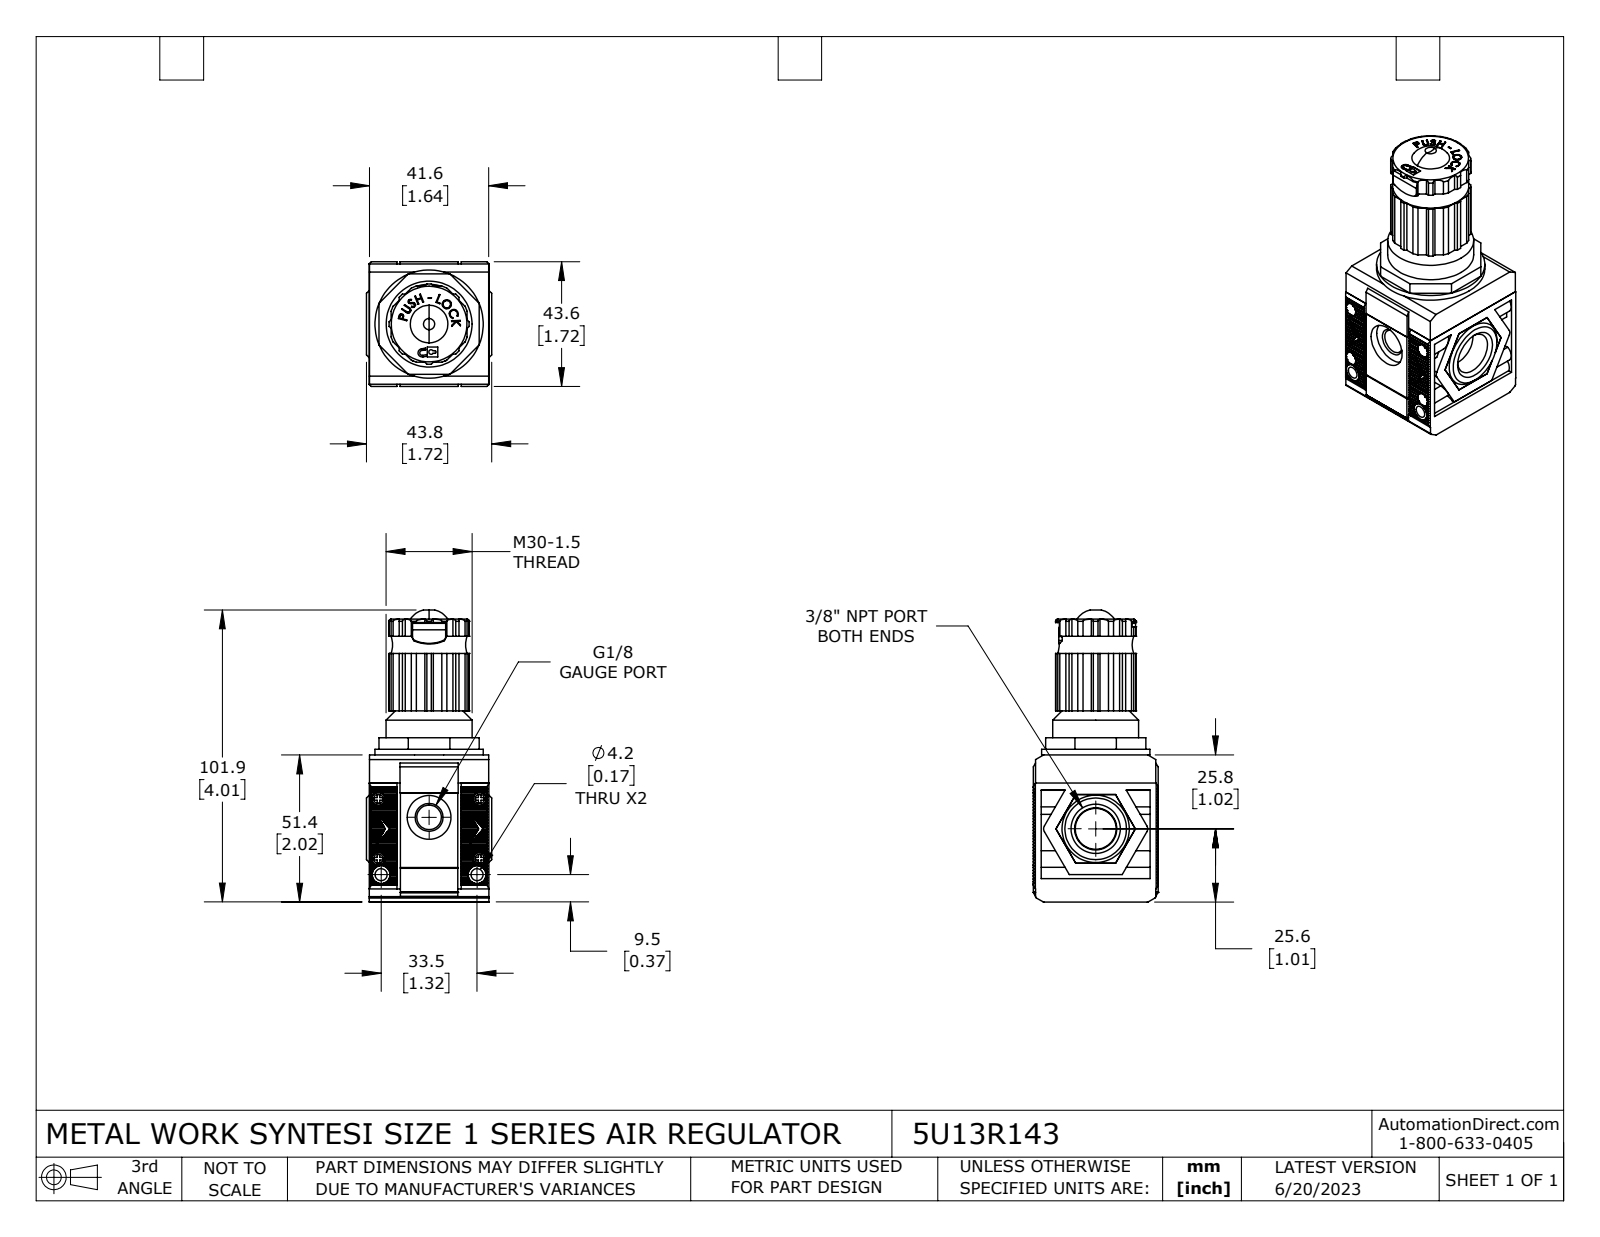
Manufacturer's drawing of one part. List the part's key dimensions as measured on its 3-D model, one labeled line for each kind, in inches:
Part name (STEP PRODUCT): 5U13R143
STEP written by: SolidWorks 2021 (CONFIG_CONTROL_DESIGN)
Units: inches
Bodies: 13 solids, 1378 faces (967 planar, 300 cylindrical, 111 other)
Overall size (bounding box): 4.016 × 1.724 × 1.717
Volume: 7.583 in³ · Surface area: 60.43 in²
Round holes (diameter × count): ⌀0.083 ×4, ⌀0.118 ×4, ⌀0.185 ×4, ⌀0.138 ×2, ⌀0.165 ×2, ⌀0.094 ×1, ⌀0.252 ×1, ⌀0.337 ×1, ⌀0.602 ×1, ⌀1.117 ×1
Round bosses / shafts (diameter × count): ⌀0.181 ×4, ⌀0.102 ×4, ⌀0.244 ×2, ⌀1.488 ×1, ⌀1.26 ×1, ⌀1.181 ×1, ⌀0.898 ×1, ⌀0.717 ×1
Partial cylindrical surfaces — rounded edges, fillets, slot ends (radius × count): R0.024 ×4, R0.122 ×4, R0.059 ×3, R0.008 ×2, R0.051 ×2, R0.079 ×2, R0.016 ×1, R0.018 ×1
Main face-to-face distances: 0.386, 1.638, 2.024, 1.642, 0.043, 0.067, 1.673, 1.575, 1.646, 0.307
Hole centre spacings: 0.222, 0.362, 0.742, 0.785, 0.823, 0.9, 1.027, 1.042
